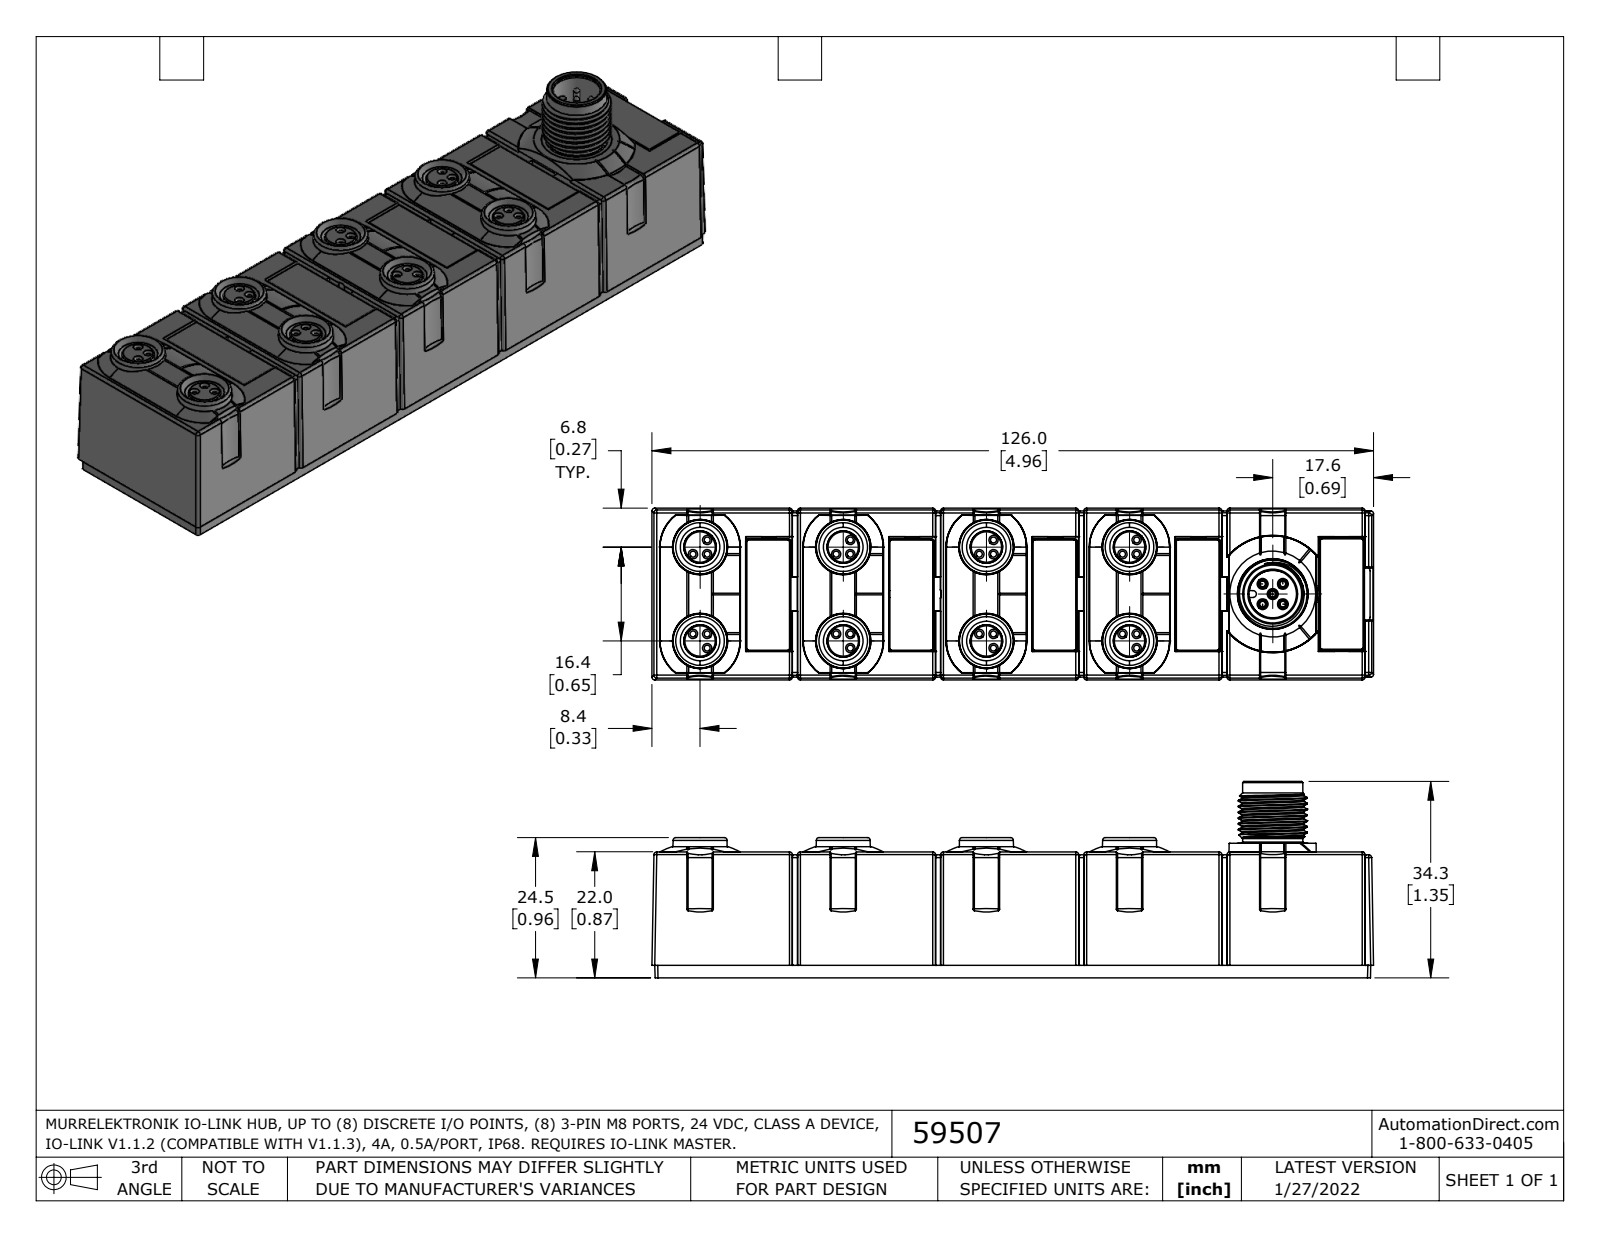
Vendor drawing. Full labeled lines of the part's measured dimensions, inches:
Part name (STEP PRODUCT): 59507
STEP written by: SolidWorks 2021 (AUTOMOTIVE_DESIGN)
Units: inches
Bodies: 1 solid, 1501 faces (524 planar, 426 cylindrical, 551 other)
Overall size (bounding box): 4.979 × 1.364 × 1.266
Volume: 5.009 in³ · Surface area: 31.54 in²
Round holes (diameter × count): ⌀0.041 ×24, ⌀0.049 ×5, ⌀0.075 ×5, ⌀0.272 ×5, ⌀0.272 ×3, ⌀0.169 ×1, ⌀0.327 ×1
Round bosses / shafts (diameter × count): ⌀0.039 ×5, ⌀0.413 ×2, ⌀0.484 ×1, ⌀0.472 ×1, ⌀0.252 ×1
Partial cylindrical surfaces — rounded edges, fillets, slot ends (radius × count): R0.02 ×93, R0.01 ×42, R0.007 ×20, R0.033 ×12, R0.591 ×12, R0.394 ×11, R0.008 ×10, R0.047 ×9
Main face-to-face distances: 0.866, 0.079, 0.787, 0.037, 0.864, 0.077, 0.038, 1.161, 1.161, 0.037
Hole centre spacings: 0.069, 0.098, 0.098, 0.548, 0.599, 1.177, 1.969, 2.953
